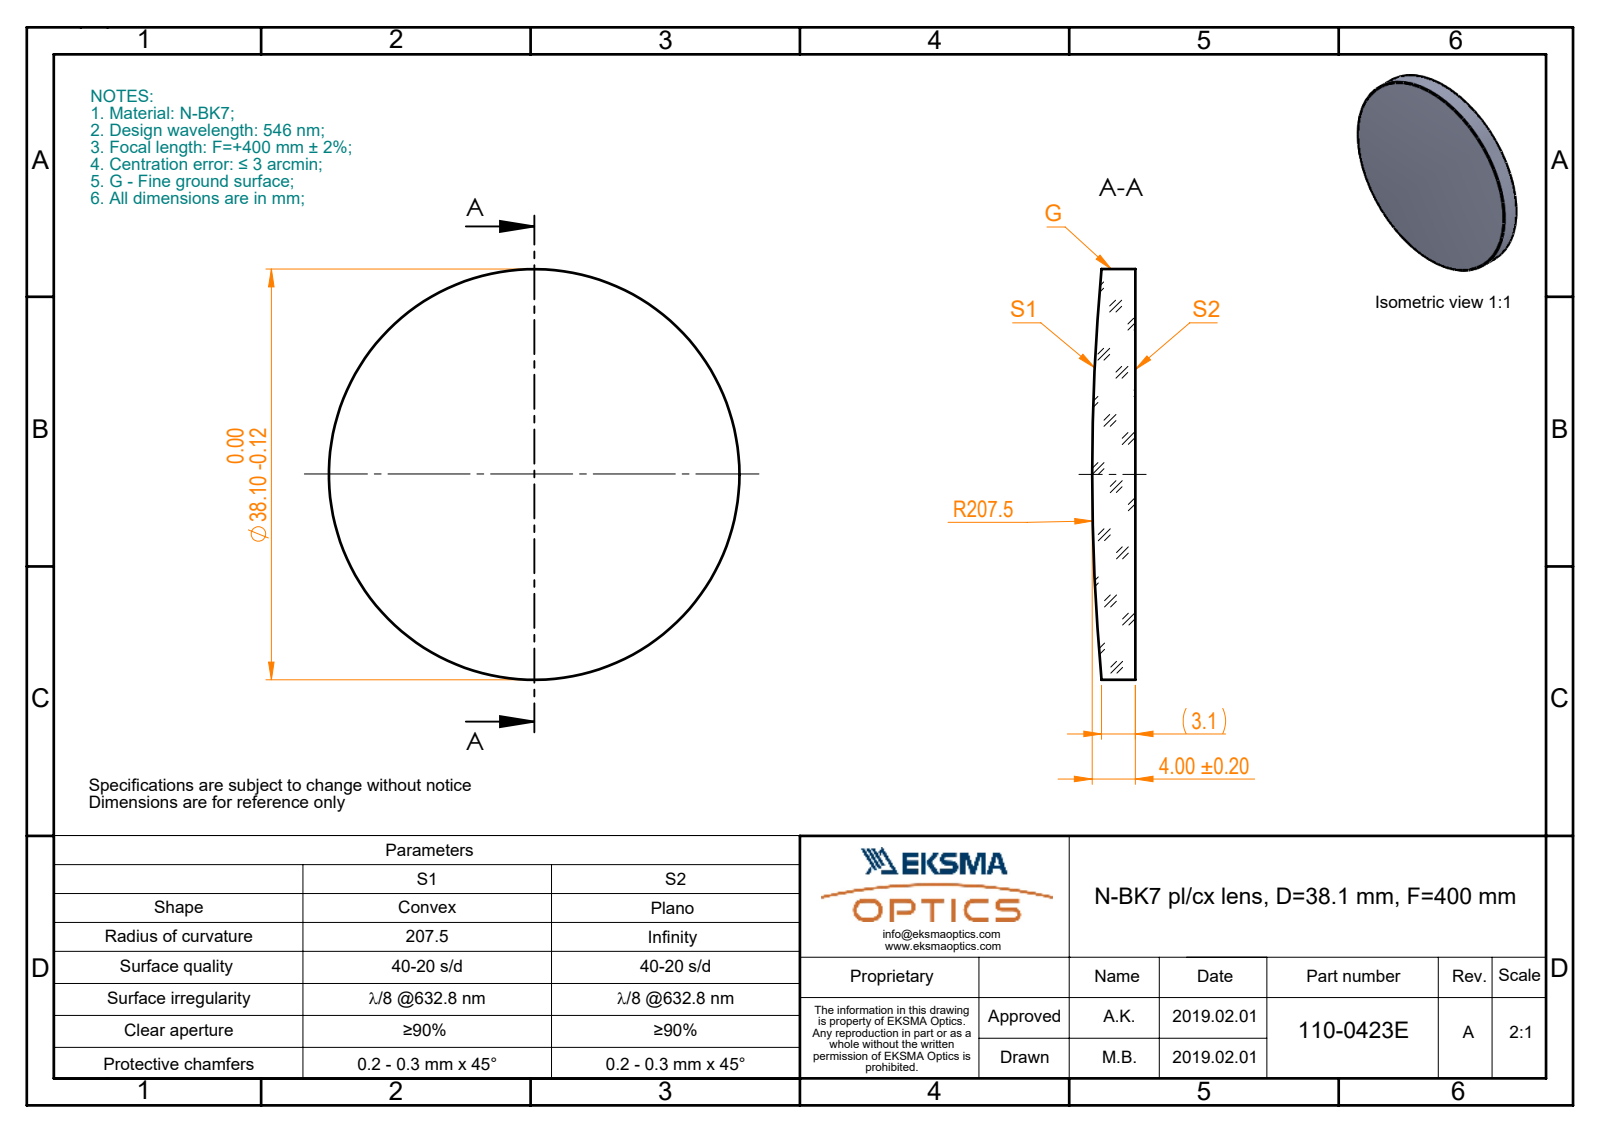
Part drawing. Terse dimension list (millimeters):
name: 110-0423E BK7 pl-cx 38.1 F400
written by: SolidWorks 2017 (CONFIG_CONTROL_DESIGN)
unit: mm
bodies: 1 solid, 5 faces (1 planar, 2 cylindrical, 2 other)
size: 38.1 × 38.1 × 4
volume: 4 061 mm³; area: 2 656 mm²
bosses: 1× ⌀38.1
